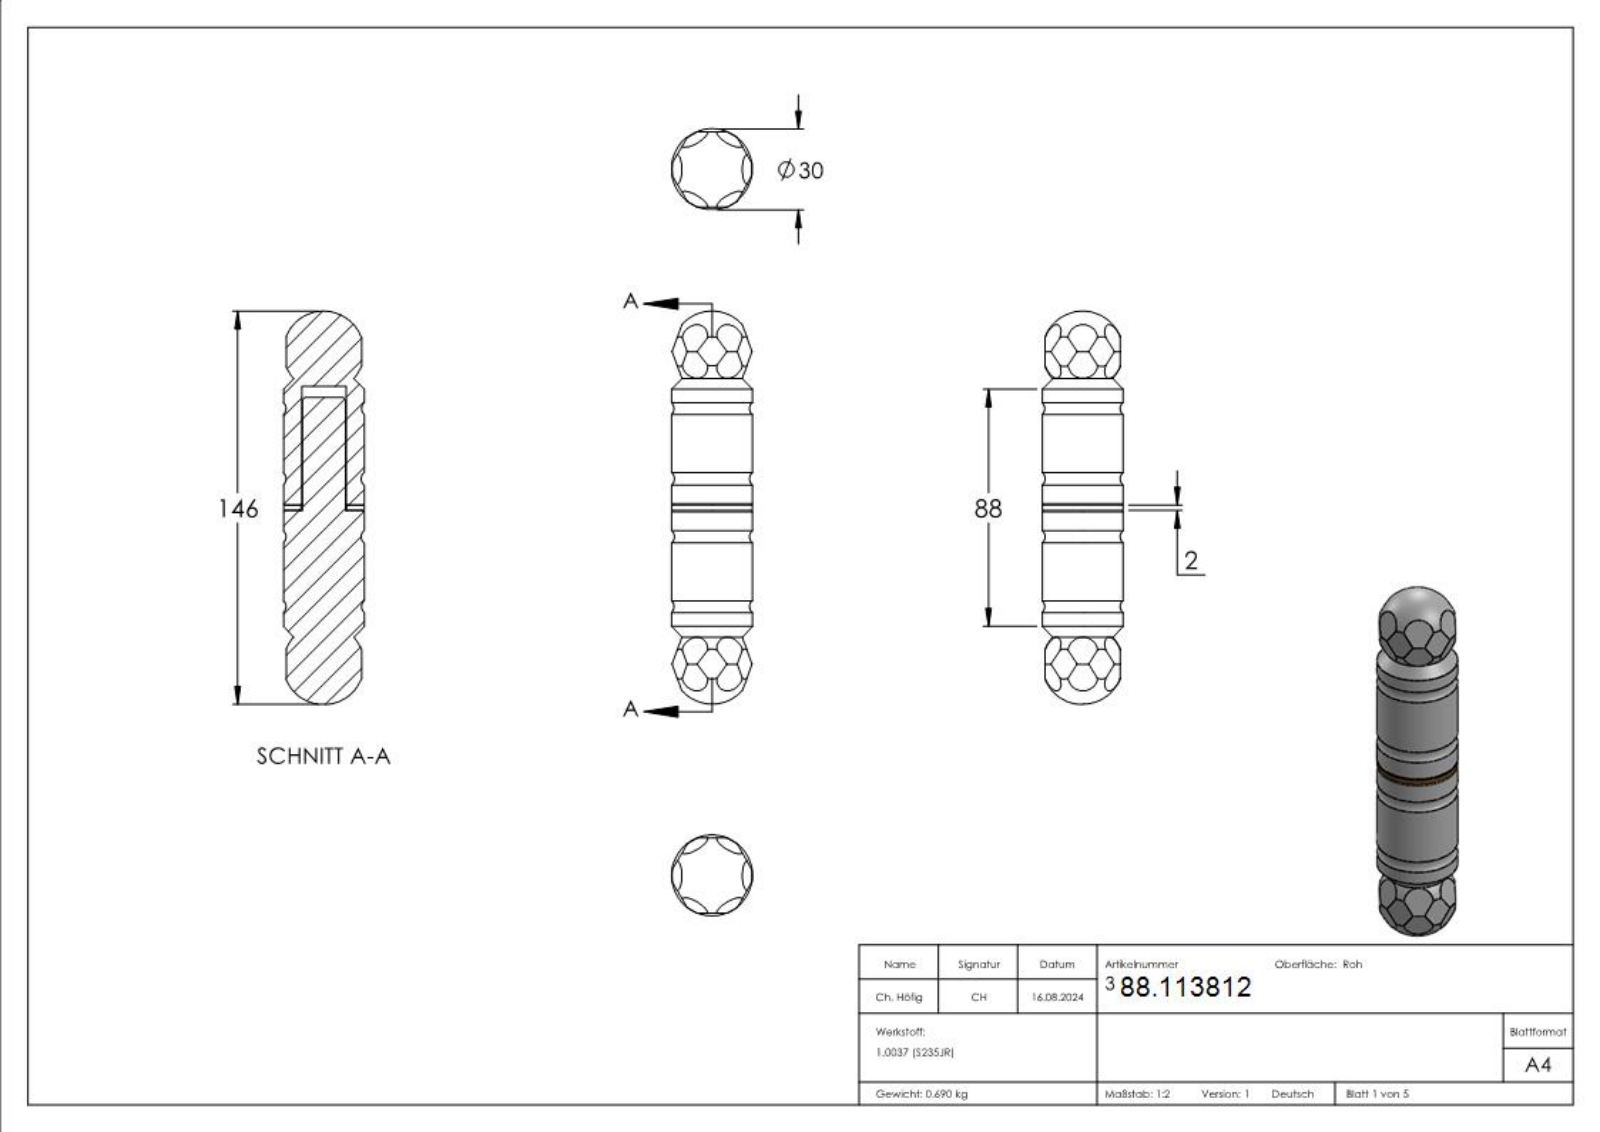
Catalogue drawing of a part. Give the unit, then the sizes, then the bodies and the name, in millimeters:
Units: millimetres
Overall size (bounding box): 146 × 30 × 30
Round holes (diameter × count): ⌀16.5 ×1, ⌀17 ×1
Round bosses / shafts (diameter × count): ⌀30 ×1, ⌀16 ×1
Partial cylindrical surfaces — rounded edges, fillets, slot ends (radius × count): R8.35 ×1
Main face-to-face distances: 27.91, 39.67, 2, 11.76, 67.58, 27.9, 46, 44, 42, 40
Volume: 88 341 mm³ · Surface area: 20 683 mm²
Bodies: 3 solids, 304 faces (133 planar, 28 cylindrical, 143 other)
Part name (STEP PRODUCT): 3810 - 3811 - 3812 Teil1-3_3812 Teil1; 3810 - 3811 - 3812 Teil1-3_3812 Teil3; 3810 - 3811 - 3812 Teil1-3_3812 Teil2; 3812
STEP written by: SolidWorks 2018 (CONFIG_CONTROL_DESIGN)
